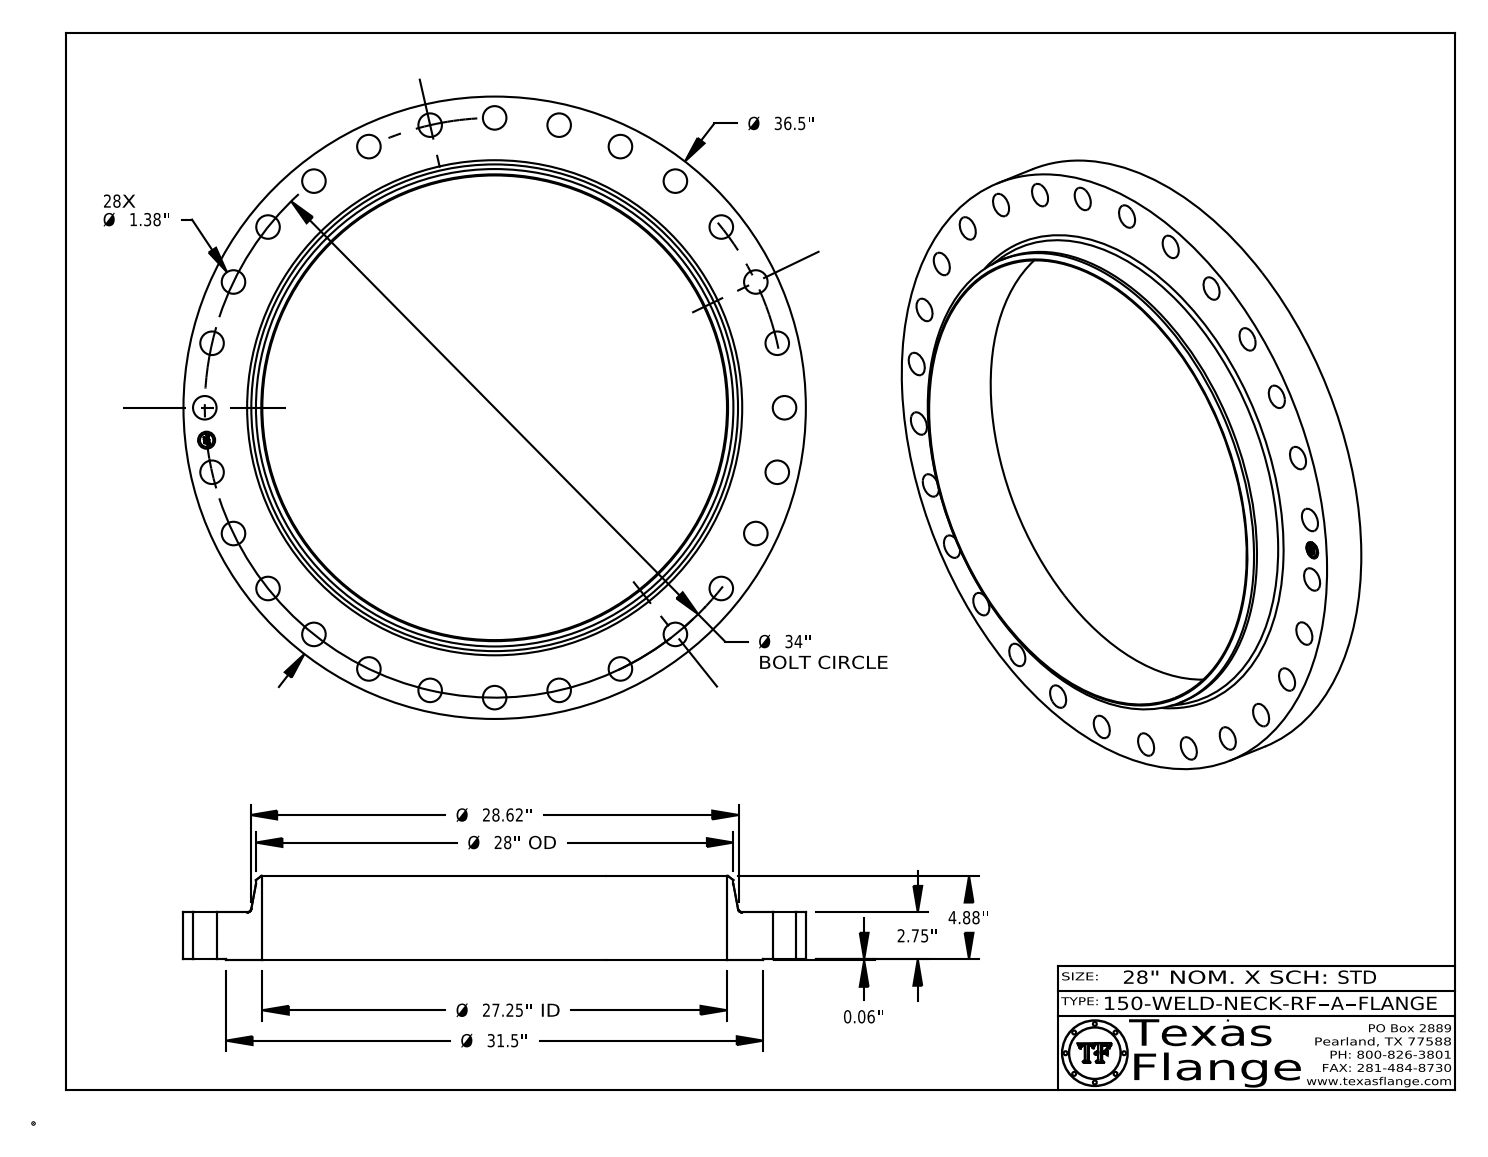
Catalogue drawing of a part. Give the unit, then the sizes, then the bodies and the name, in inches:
Units: inches
Overall size (bounding box): 36.5 × 36.5 × 4.943
Round holes (diameter × count): ⌀1.38 ×28, ⌀1 ×1, ⌀27.25 ×1
Round bosses / shafts (diameter × count): ⌀0.061 ×8, ⌀36.5 ×1, ⌀31.5 ×1, ⌀28 ×1, ⌀0.788 ×1
Main face-to-face distances: 2.75, 0.063, 2.813, 4.943, 4.88, 2.13, 0.015, 2.798, 2.735, 2.145
Hole centre spacings: 3.807, 7.566, 30.633, 33.786, 17, 11.23, 18.089, 21.198
Volume: 1 260 in³ · Surface area: 2 065 in²
Bodies: 1 solid, 459 faces (369 planar, 84 cylindrical, 6 other)
Part name (STEP PRODUCT): 150-WELD-NECK-RF, Series A
STEP written by: CATIA V5 STEP AP214 (AUTOMOTIVE_DESIGN)
